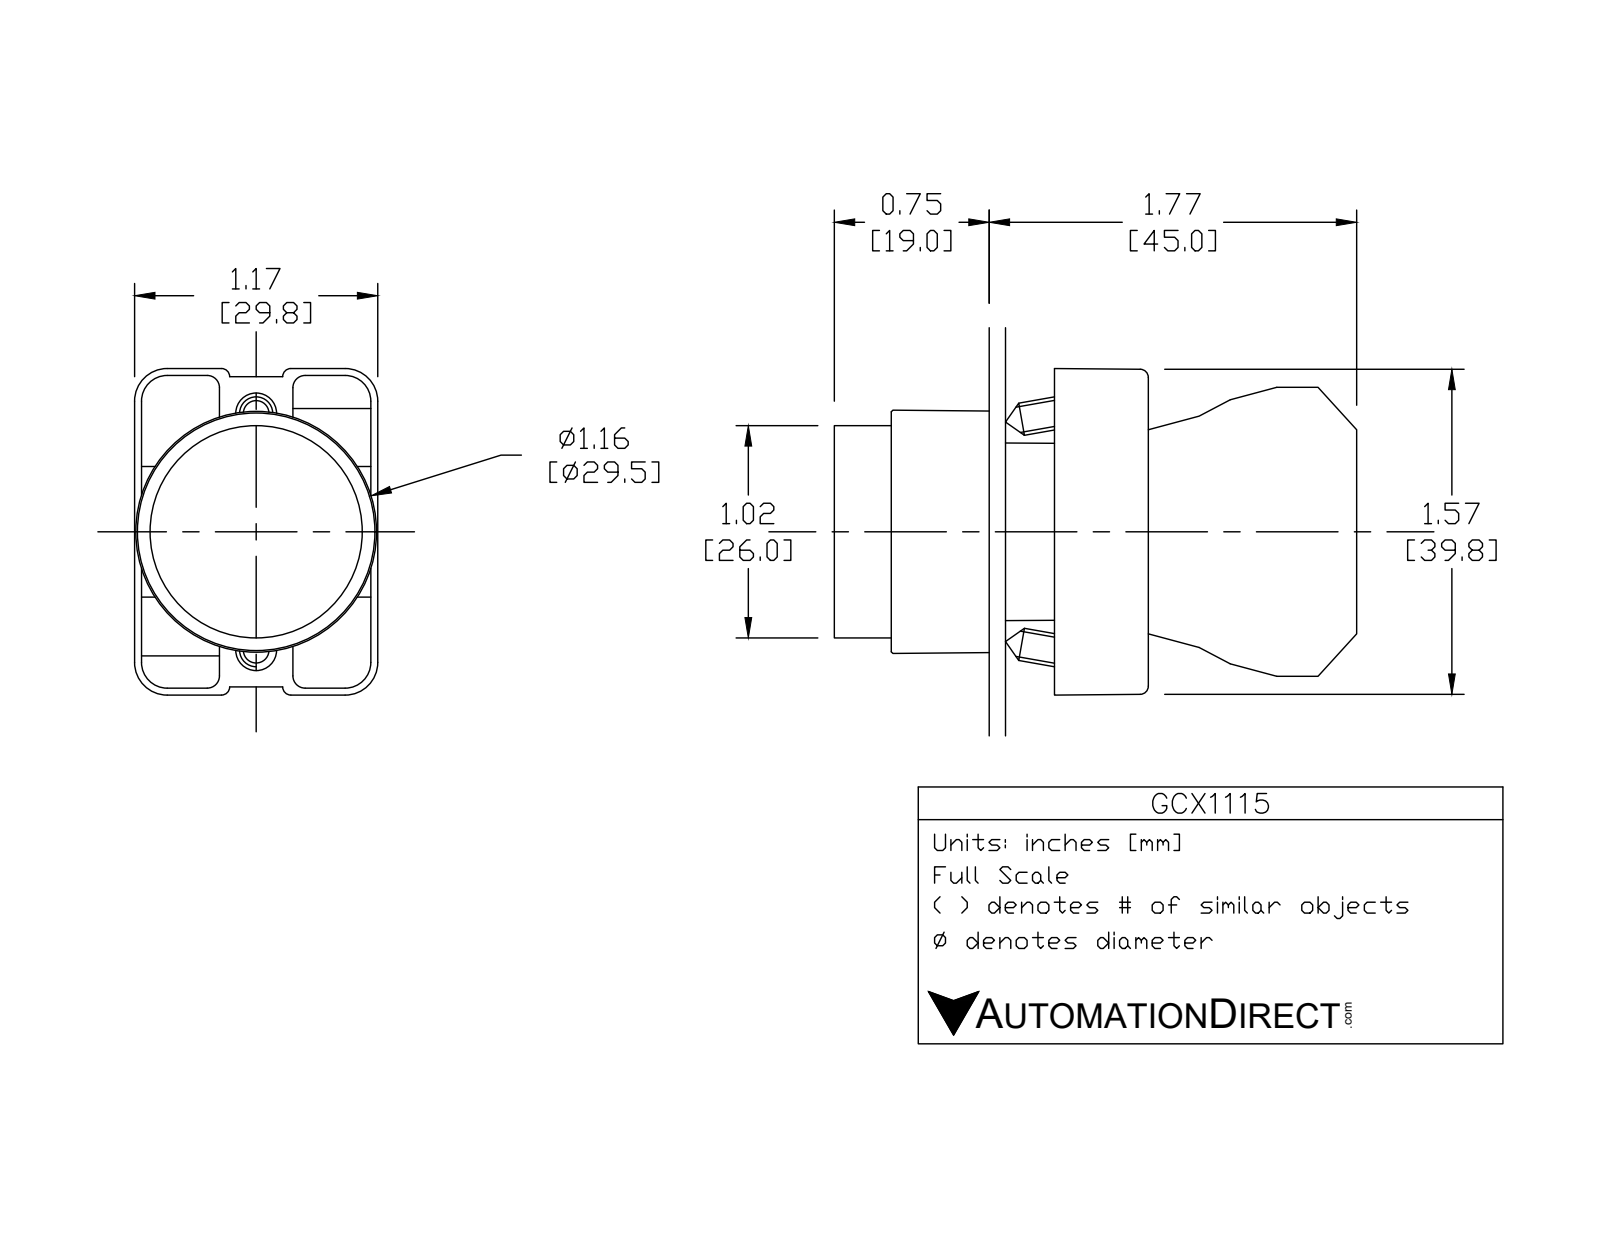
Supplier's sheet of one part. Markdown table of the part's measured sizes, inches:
| quantity | value |
| --- | --- |
| part name | ecx1029; ecx1040; GCX1115 OPERATOR; GCX1115 |
| STEP written by | SolidWorks 2016 (AUTOMOTIVE_DESIGN) |
| units | inches |
| bodies | 6 solids, 383 faces (222 planar, 132 cylindrical, 29 other) |
| overall size | 2.492 × 1.581 × 1.177 |
| volume | 1.584 in³ |
| surface area | 26.47 in² |
| round holes (diameter × count) | 0.079 × 2, 0.124 × 2, 0.13 × 2, 0.087 × 1, 0.197 × 1, 0.878 × 1, 0.888 × 1, 1.024 × 1 |
| round bosses / shafts (diameter × count) | 0.157 × 2, 1.175 × 1, 1.004 × 1, 0.945 × 1, 0.856 × 1, 0.78 × 1 |
| partial cylindrical surfaces (radius × count) | 0.059 × 24, 0.041 × 12, 0.124 × 12, 0.157 × 12, 0.039 × 4, 0.128 × 2, 0.02 × 1, 0.063 × 1 |
| main face-to-face distances | 0.579, 0.033, 1.193, 0.031, 0.472, 0.72, 0.276, 0.689, 0.598, 1.161 |
| hole center spacings | 0.236, 0.544, 0.472, 0.49 |
